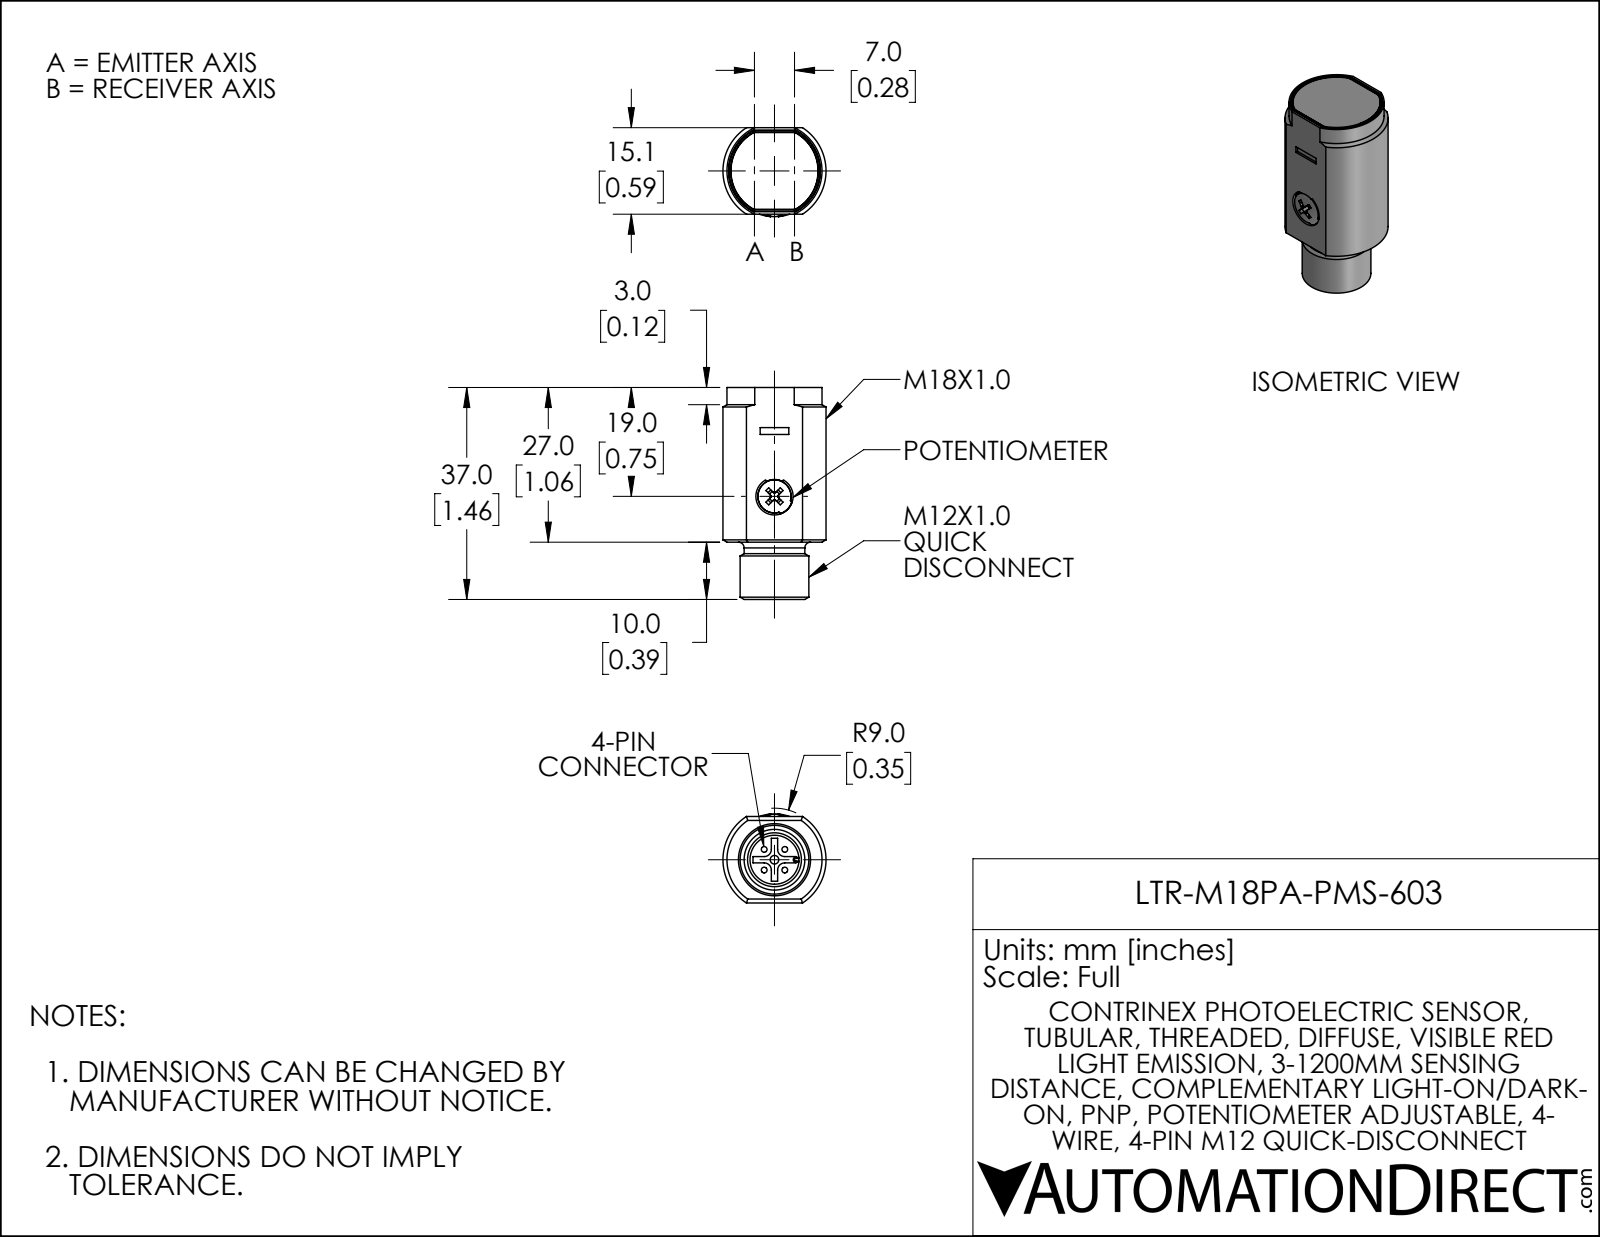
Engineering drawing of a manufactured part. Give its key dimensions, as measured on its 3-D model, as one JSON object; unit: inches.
{"part_name": "LTR-M18PA-PMS-603", "step_written_by": "SolidWorks 2021 (AUTOMOTIVE_DESIGN)", "units": "inches", "bodies": {"solids": 1, "faces": 148, "planar": 75, "cylindrical": 53, "other": 20}, "overall_size": [1.457, 0.709, 0.611], "volume_in3": 0.417, "surface_area_in2": 4.272, "round_holes": [[0.059, 1], [0.256, 1], [0.336, 1]], "round_bosses_or_shafts": [[0.039, 4], [0.472, 1], [0.417, 1]], "partial_cylinders_radius": [[0.014, 8], [0.028, 8], [0.006, 4], [0.024, 4], [0.049, 4], [0.008, 2], [0.017, 1], [0.116, 1]], "face_to_face_distances": [0.594, 1.061, 0.047, 1.108, 0.016, 1.063, 1.11, 1.457, 1.455, 0.394]}
